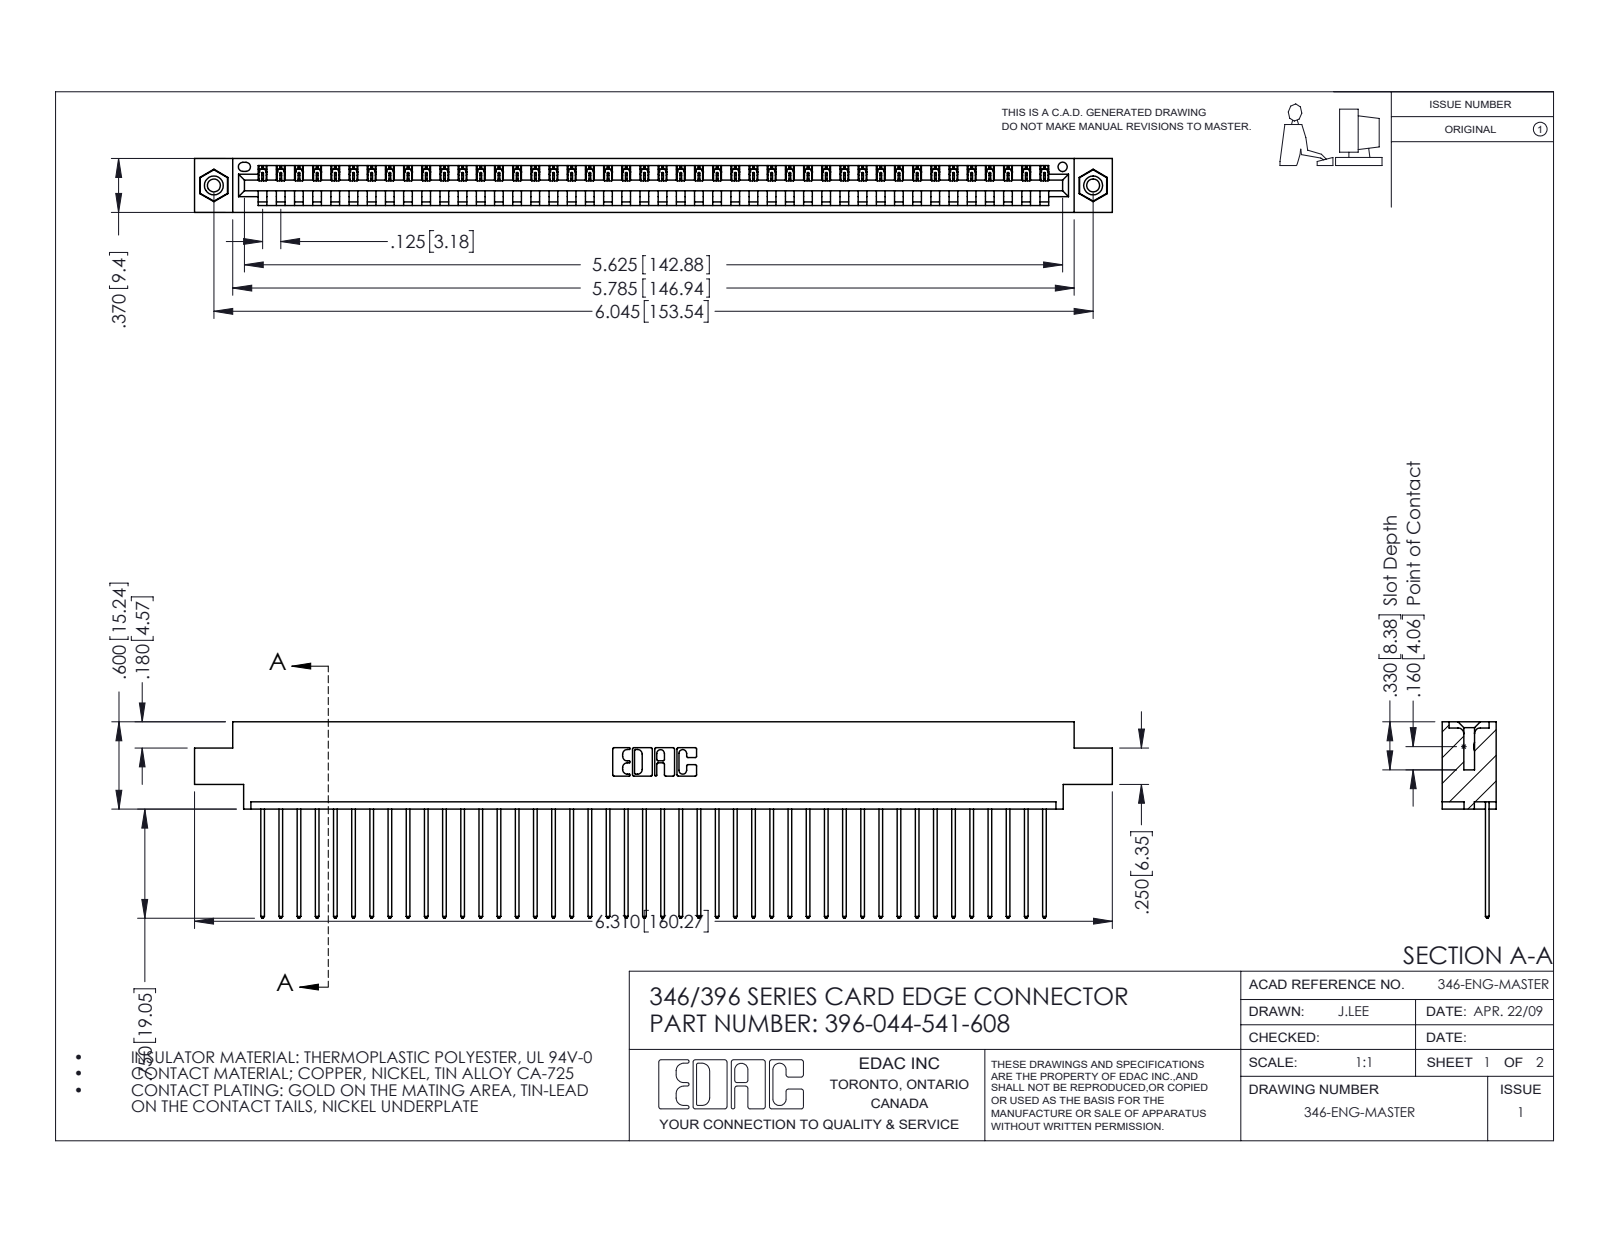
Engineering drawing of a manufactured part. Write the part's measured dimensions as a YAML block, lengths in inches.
part_name: "345-292-001_345-293-141; 346 Part_0.170 Offset - 0.156 Dia-TI; 345-250-001_345-250-003-102; 396-044-541-608"
step_written_by: "SolidWorks 2016 (CONFIG_CONTROL_DESIGN)"
units: inches
bodies: {solids: 47, faces: 2738, planar: 1872, cylindrical: 850, other: 16}
overall_size: [6.31, 1.35, 0.37]
volume: 0.936
surface_area: 31.38
round_holes:
  - {diameter: 0.089, count: 2}
  - {diameter: 0.125, count: 2}
  - {diameter: 0.156, count: 2}
  - {diameter: 0.064, count: 1}
round_bosses_or_shafts:
  - {diameter: 0.155, count: 2}
partial_cylinders:
  - {radius: 0.006, count: 88}
  - {radius: 0.01, count: 88}
  - {radius: 0.01, count: 22}
  - {radius: 0.007, count: 6}
  - {radius: 0.031, count: 6}
  - {radius: 0.026, count: 3}
  - {radius: 0.031, count: 2}
  - {radius: 0.04, count: 2}
face_to_face_distances: [0.048, 0.322, 0.37, 0.25, 0.072, 0.298, 0.025, 0.222, 0.148, 0.1]
hole_center_spacings: [0.246, 5.836, 6.045]
